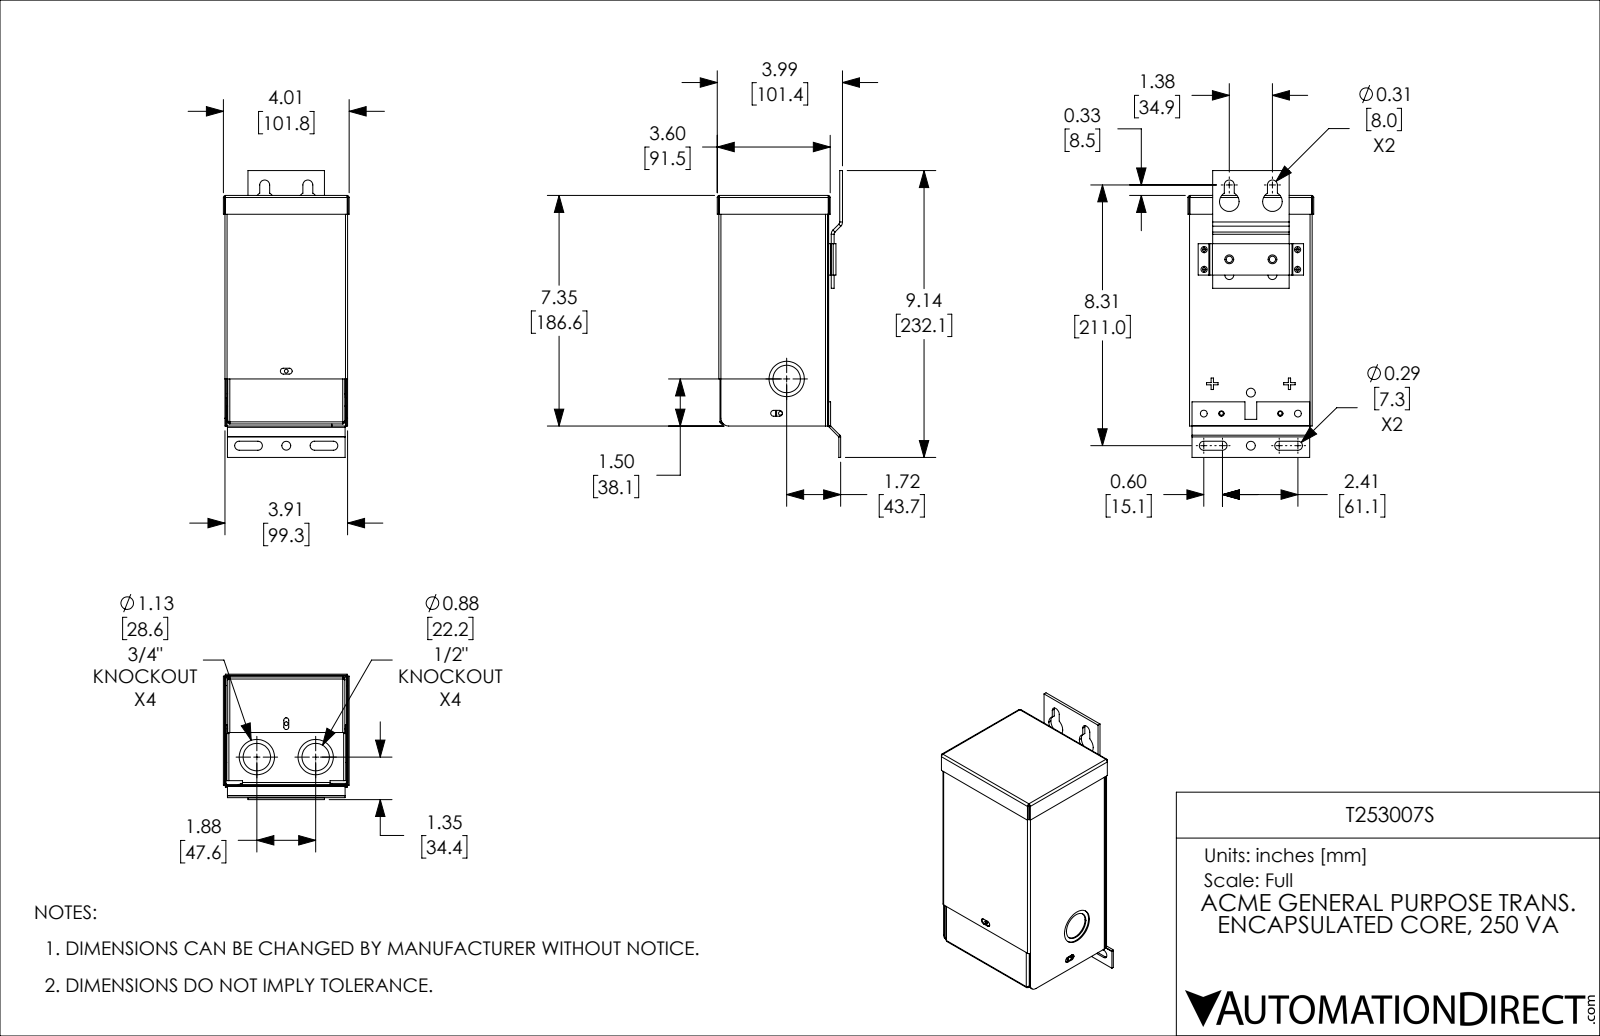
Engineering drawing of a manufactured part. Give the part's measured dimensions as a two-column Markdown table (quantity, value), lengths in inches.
| quantity | value |
| --- | --- |
| part name | T253007S |
| STEP written by | SolidWorks 2021 (CONFIG_CONTROL_DESIGN) |
| units | inches |
| bodies | 7 solids, 528 faces (326 planar, 154 cylindrical, 48 other) |
| overall size | 9.137 × 4.008 × 3.993 |
| volume | 6.9 in³ |
| surface area | 352.5 in² |
| round holes (diameter × count) | 0.12 × 5, 0.281 × 3, 0.281 × 3, 0.875 × 3, 1.125 × 3, 0.171 × 2, 0.187 × 2, 0.201 × 2, 0.218 × 2, 0.625 × 2, 1.125 × 1 |
| round bosses / shafts (diameter × count) | 1.197 × 3, 0.947 × 3 |
| partial cylindrical surfaces (radius × count) | 0.031 × 16, 0.067 × 16, 0.094 × 8, 0.026 × 4, 0.086 × 4, 0.144 × 4, 0.017 × 2, 0.077 × 2 |
| main face-to-face distances | 0.036, 3.464, 3.874, 3.428, 3.91, 3.839, 3.5, 0.06, 7.242, 7.182 |
| hole center spacings | 1.375, 0.5, 0.502, 0.562, 0.563, 1.145, 1.151, 1.376 |
